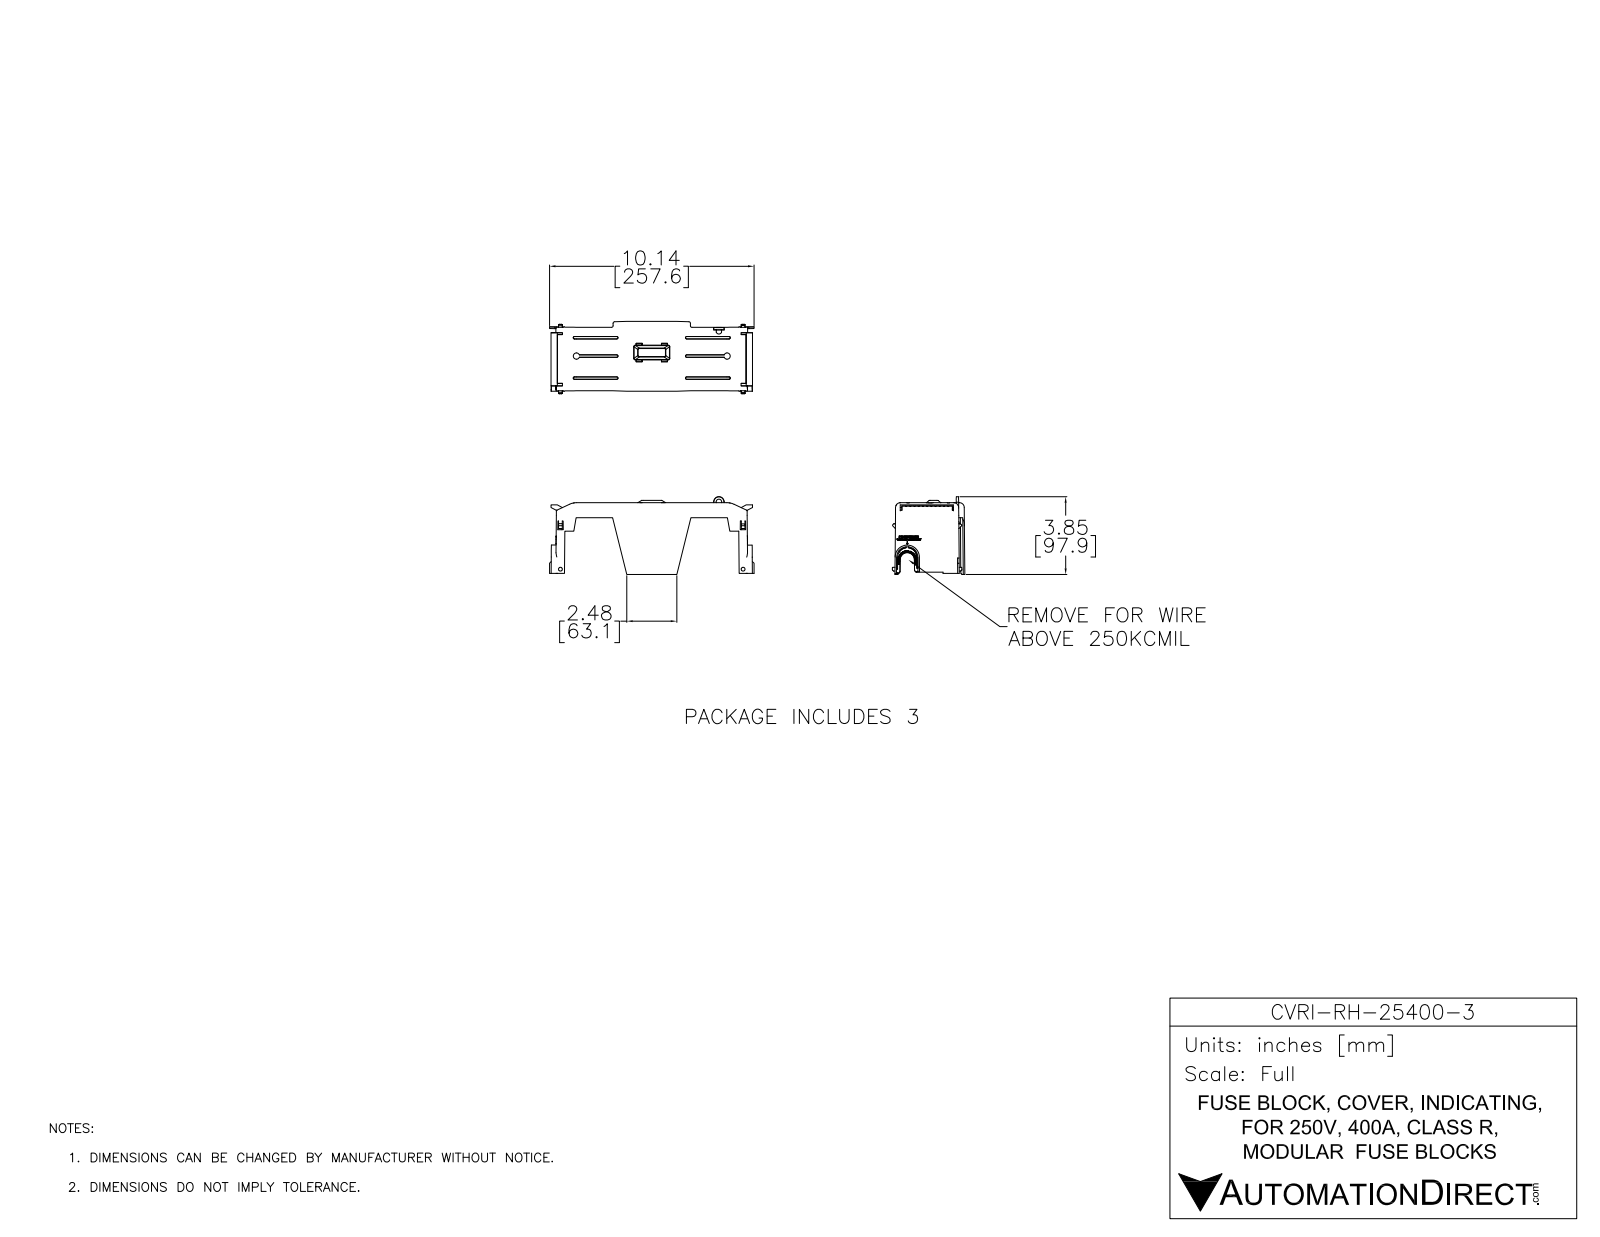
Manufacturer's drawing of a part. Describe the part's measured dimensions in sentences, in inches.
The part is named "CVRI-RH-25400-3". Its 3-D file was written by "SolidWorks 2017 (AUTOMOTIVE_DESIGN)". It is 1 solid with 2380 faces: 1598 planar, 106 cylindrical and 676 other. Overall it measures 10.143 by 3.853 by 3.593 inches. Its volume is 7.778 cubic inches and its surface area 207.6 square inches. Round holes: 1 of diameter 0.276. Partial cylindrical surfaces (rounded edges, fillets, slot ends): 19 of radius 0.039, 8 of radius 0.118, 7 of radius 0.157, 7 of radius 0.236, 6 of radius 0.079, 2 of radius 0.01, 2 of radius 0.02, 2 of radius 0.232. The main face-to-face distances are 0.079, 0.276, 0.197, 0.354, 0.118, 0.669, 0.392, 1.338, 0.24, 1.098.
